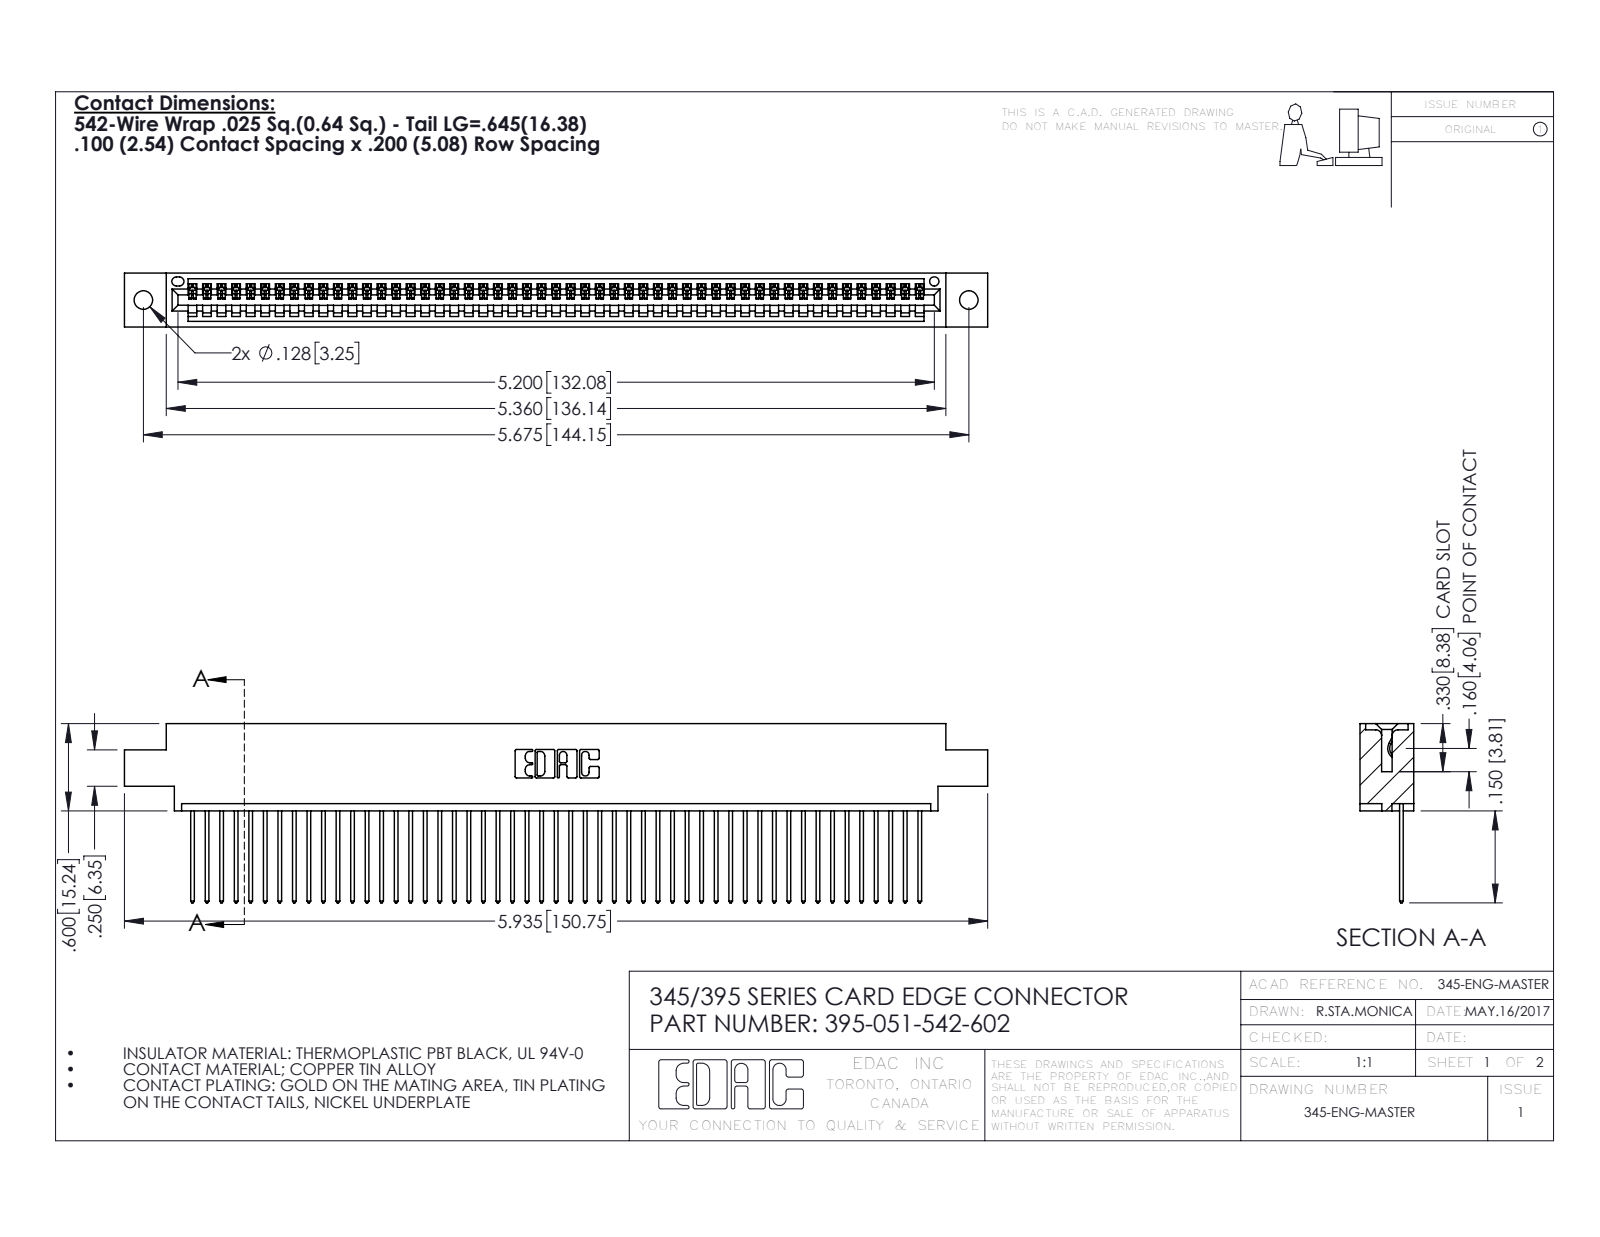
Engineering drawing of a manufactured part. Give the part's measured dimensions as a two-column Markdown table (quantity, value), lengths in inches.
| quantity | value |
| --- | --- |
| part name | 395-051-542-602; 345-292-001_345-293-142; 345 Part_0.170 Offset - 0.128 Dia |
| STEP written by | SolidWorks 2016 (CONFIG_CONTROL_DESIGN) |
| units | inches |
| bodies | 52 solids, 3088 faces (2124 planar, 964 cylindrical, 0 other) |
| overall size | 5.935 × 1.232 × 0.37 |
| volume | 0.876 in³ |
| surface area | 30.65 in² |
| round holes (diameter × count) | 0.128 × 2, 0.064 × 1 |
| partial cylindrical surfaces (radius × count) | 0.006 × 102, 0.01 × 102, 0.01 × 22, 0.007 × 6, 0.031 × 6, 0.026 × 3, 0.031 × 2, 0.04 × 2 |
| main face-to-face distances | 0.072, 0.298, 0.37, 0.098, 0.272, 0.025, 0.2, 0.225, 0.175, 0.149 |
| hole center spacings | 0.27, 5.439, 5.675 |
